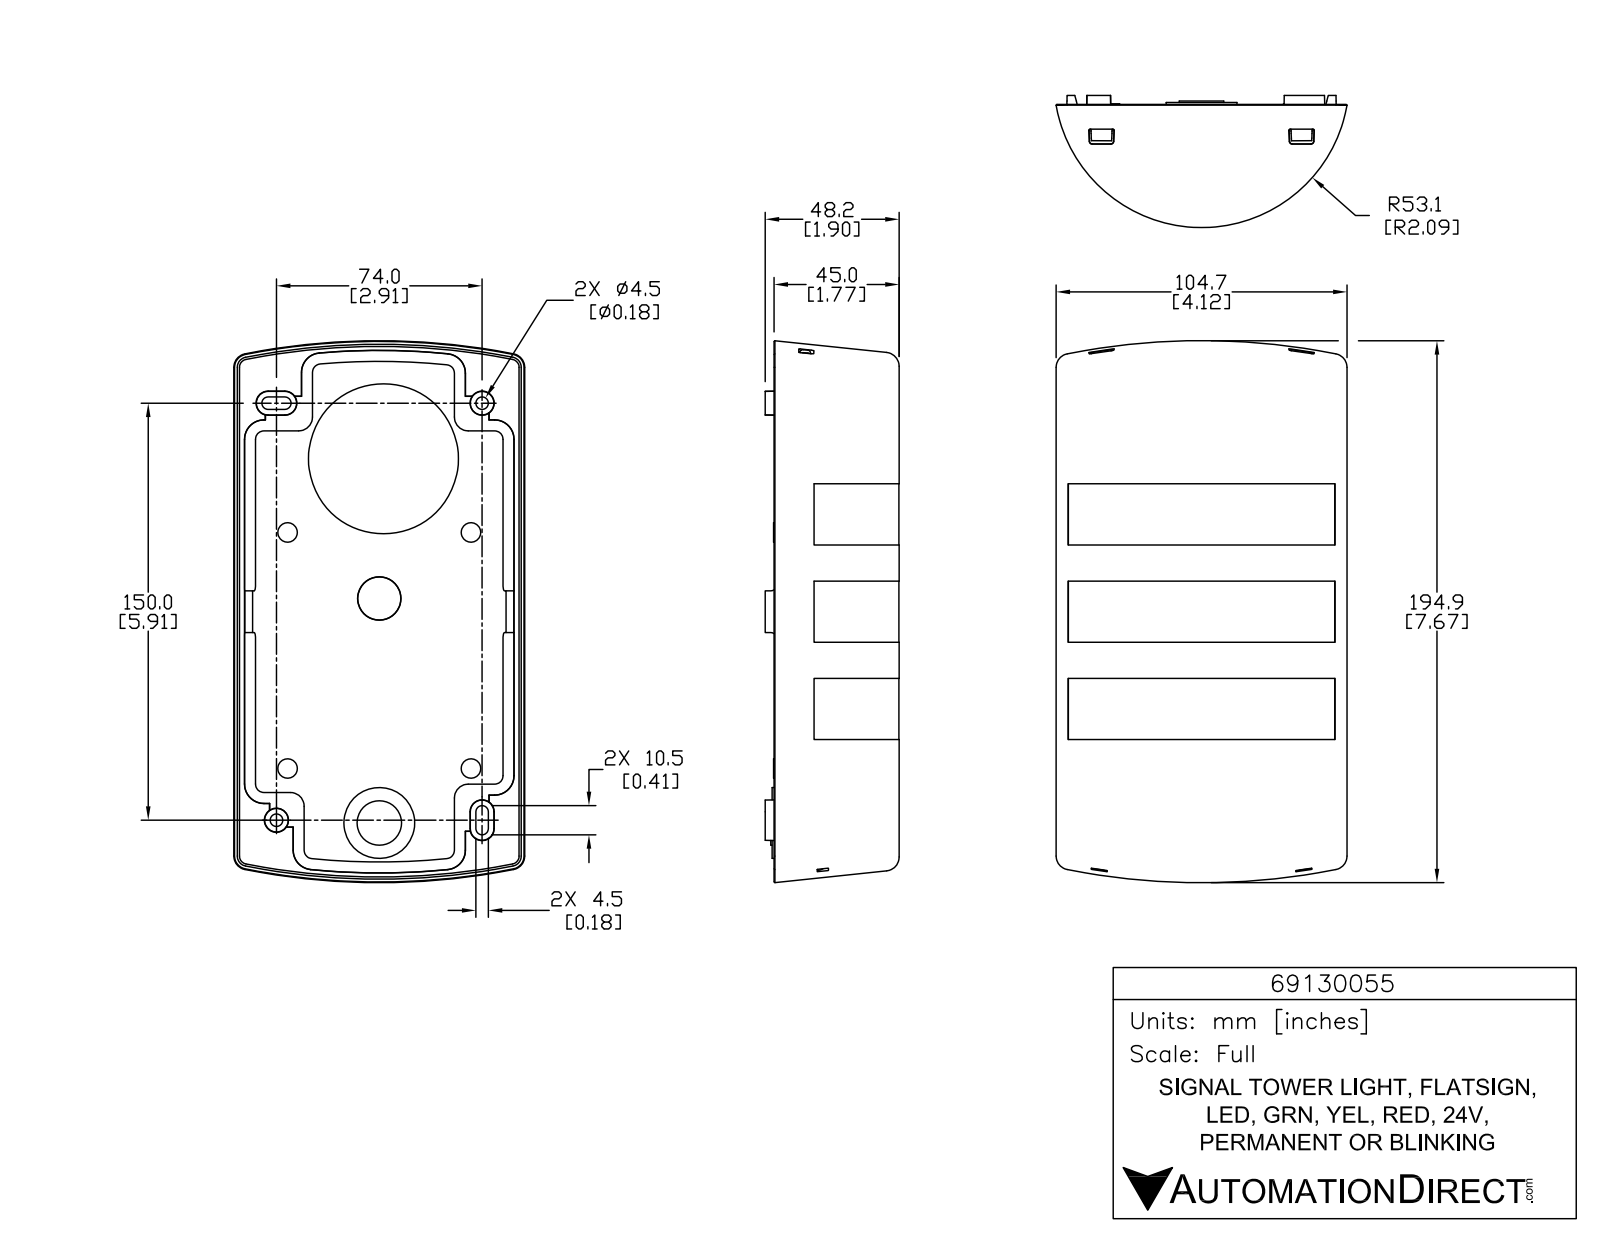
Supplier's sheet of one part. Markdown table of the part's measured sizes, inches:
| quantity | value |
| --- | --- |
| part name | 69130055 |
| STEP written by | SolidWorks 2017 (AUTOMOTIVE_DESIGN) |
| units | inches |
| bodies | 1 solid, 1074 faces (520 planar, 128 cylindrical, 426 other) |
| overall size | 7.675 × 4.122 × 1.901 |
| volume | 38.36 in³ |
| surface area | 92.68 in² |
| round holes (diameter × count) | 0.089 × 1 |
| round bosses / shafts (diameter × count) | 2.126 × 1, 1.004 × 1, 0.63 × 1, 0.514 × 1, 0.128 × 1 |
| partial cylindrical surfaces (radius × count) | 0.039 × 12, 0.012 × 4, 0.008 × 3, 0.008 × 2, 0.018 × 2, 0.019 × 2, 0.019 × 2, 0.02 × 2 |
| main face-to-face distances | 0.031, 0.079, 0.047, 0.11, 0.063, 0.157, 0.039, 0.02, 0.138, 0.118 |
